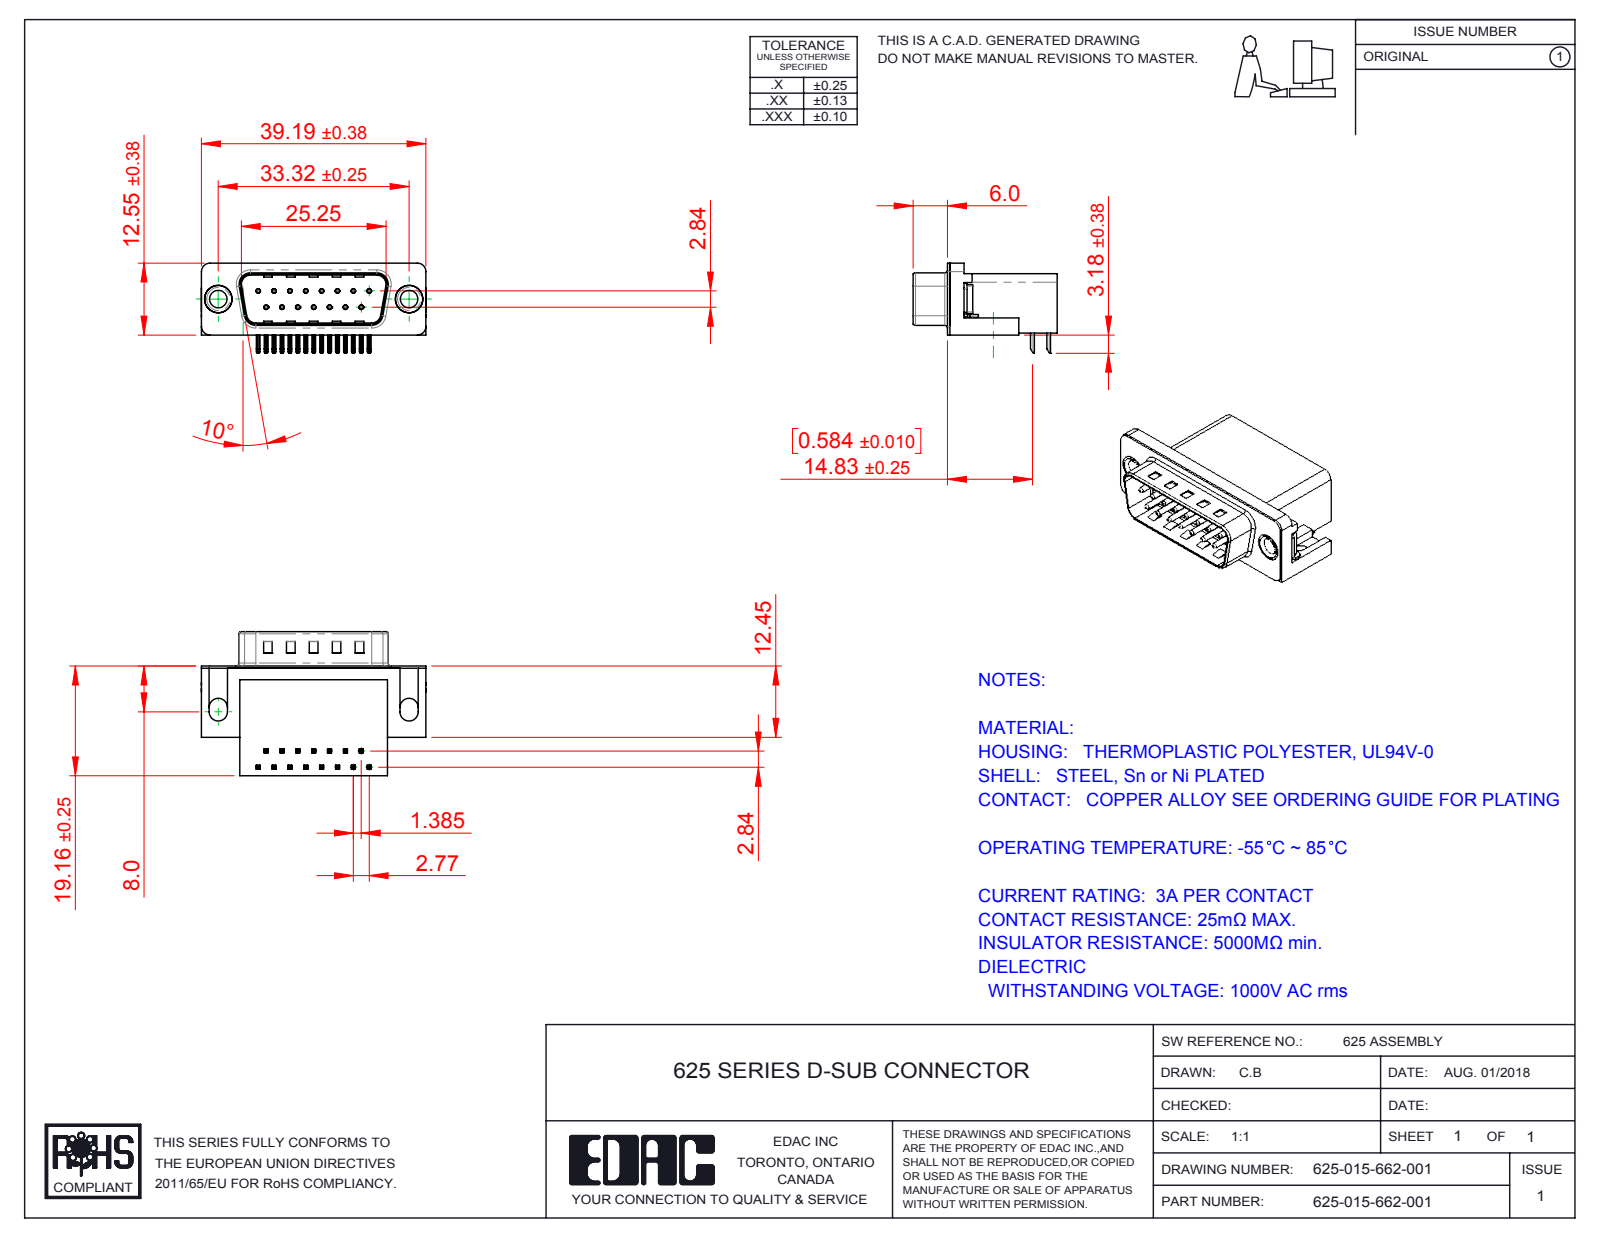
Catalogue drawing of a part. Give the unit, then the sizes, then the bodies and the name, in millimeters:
Units: millimetres
Overall size (bounding box): 39.22 × 25.16 × 15.73
Round holes (diameter × count): ⌀0.35 ×15, ⌀0.8 ×15, ⌀3.05 ×2, ⌀4 ×2, ⌀4.8 ×2, ⌀5 ×2
Round bosses / shafts (diameter × count): ⌀0.75 ×15, ⌀4.9 ×2, ⌀4.75 ×2, ⌀3.85 ×2
Partial cylindrical surfaces — rounded edges, fillets, slot ends (radius × count): R0.25 ×68, R0.12 ×30, R1 ×16, R0.5 ×9, R1.6 ×8, R1.5 ×6, R0.9 ×4, R2 ×4
Main face-to-face distances: 0.4, 10.35, 18.76, 2.1, 19.16, 10.46, 1.7, 10.86, 8.76, 16.26
Hole centre spacings: 3.16, 2.77, 5.54, 8.31, 11.08, 5.03, 5.04, 7.48
Volume: 6 203 mm³ · Surface area: 6 267 mm²
Bodies: 21 solids, 1437 faces (895 planar, 425 cylindrical, 117 other)
Part name (STEP PRODUCT): 625 Thru Hole Rivet; 625 Non Board Mount; 625-015-662-001; 625 Housing_15 Socket (+3 more)
STEP written by: SolidWorks 2016 (CONFIG_CONTROL_DESIGN)
